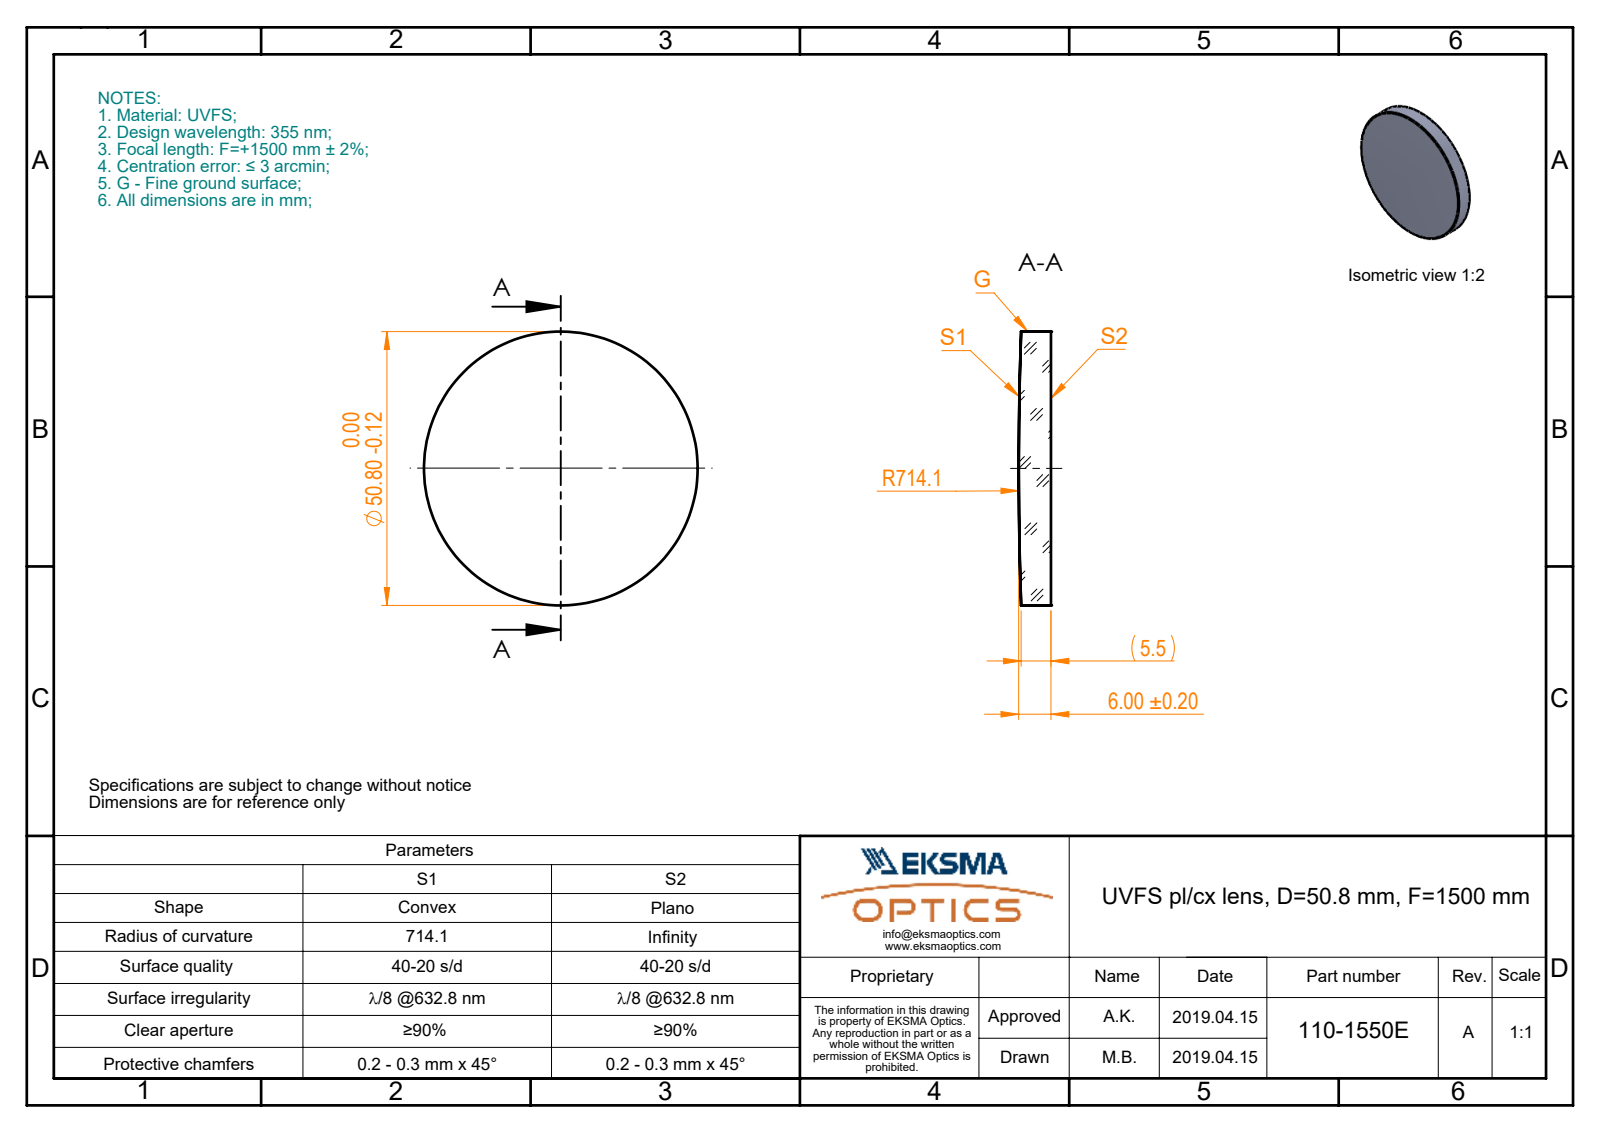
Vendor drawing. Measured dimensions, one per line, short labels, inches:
name: 110-1550E UVFS pl-cx 50.8 F1500
written by: SolidWorks 2017 (CONFIG_CONTROL_DESIGN)
unit: in
bodies: 1 solid, 5 faces (1 planar, 2 cylindrical, 2 other)
size: 2 × 2 × 0.236
volume: 0.714 in³; area: 7.657 in²
bosses: 1× ⌀2
